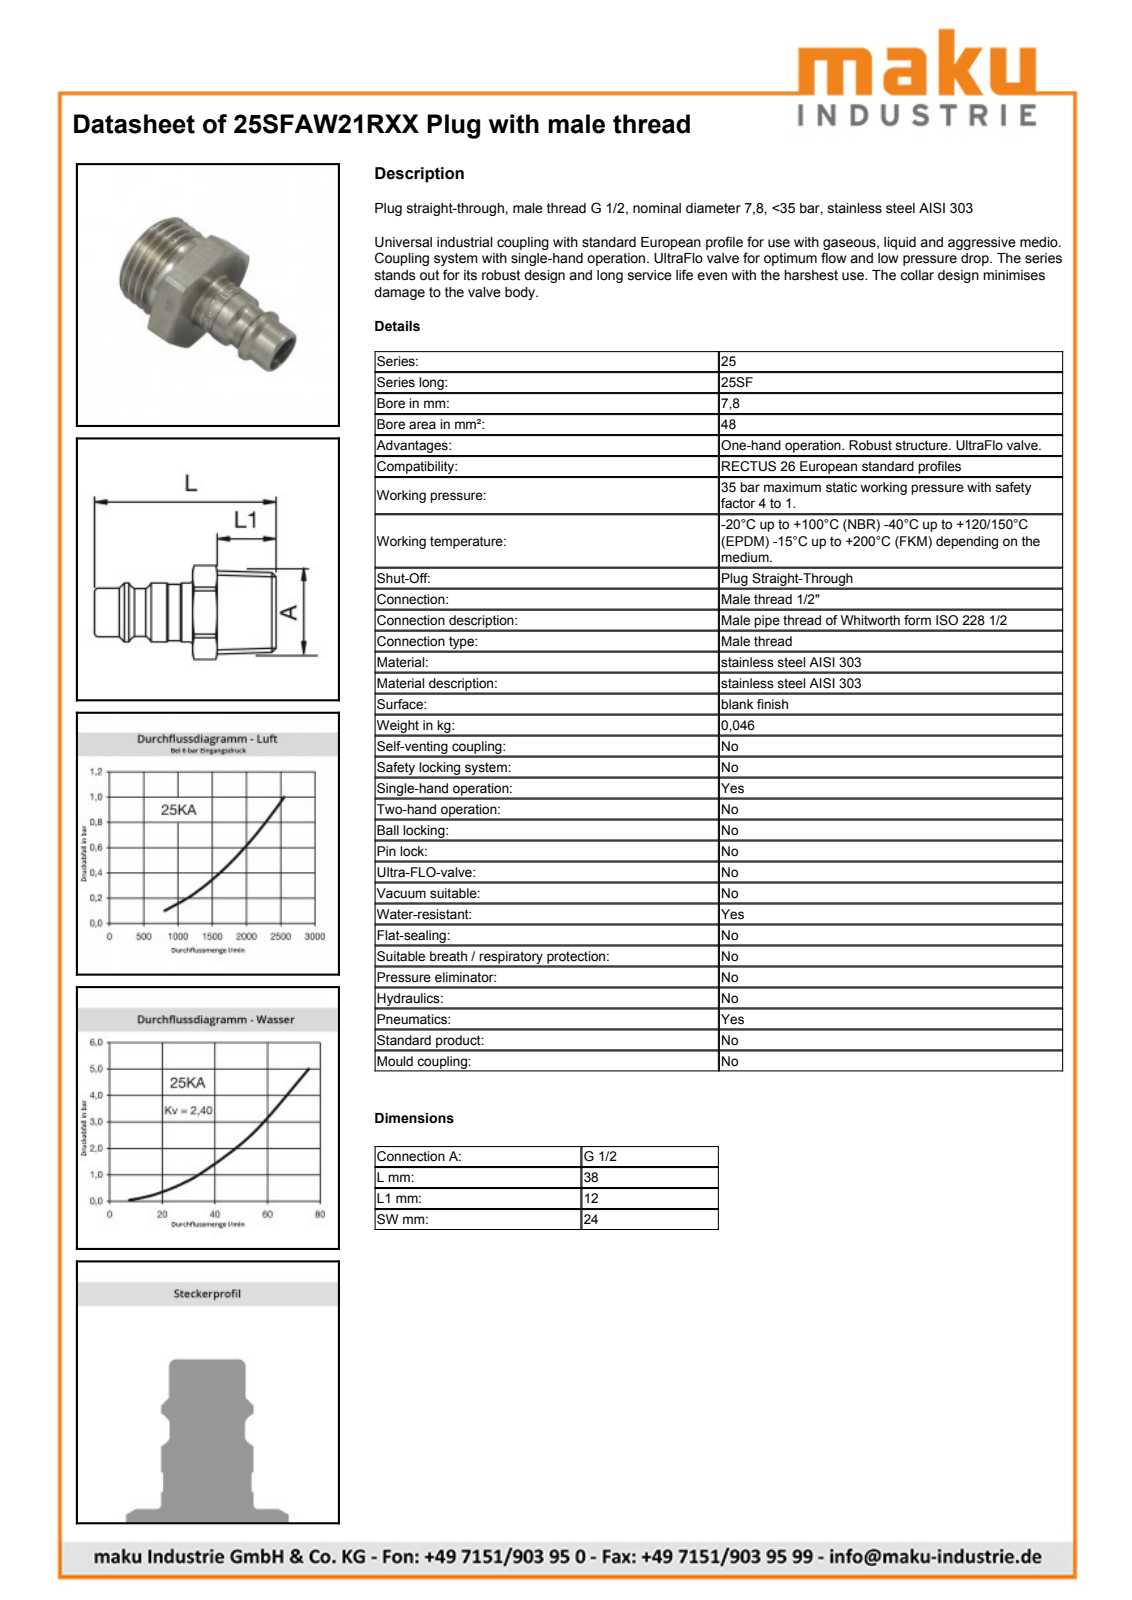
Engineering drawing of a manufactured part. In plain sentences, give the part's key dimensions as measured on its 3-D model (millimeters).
The part is named "D104286". Its 3-D file was written by "Autodesk Inventor 2011 (AUTOMOTIVE_DESIGN)". It is 1 solid with 295 faces: 109 planar, 33 cylindrical and 153 other. Overall it measures 38 by 27.05 by 24 millimeters. Its volume is 6 323 cubic millimeters and its surface area 3 784 square millimeters. Round holes: 1 of diameter 7.85. Round bosses or shafts: 1 of diameter 20.95, 1 of diameter 12, 1 of diameter 11.5, 1 of diameter 9.9, 1 of diameter 9.75. Partial cylindrical surfaces (rounded edges, fillets, slot ends): 1 of radius 5.65, 1 of radius 13.53. The main face-to-face distances are 24, 6, 18, 12, 20, 26, 38, 17.23, 2.77, 8.77.
